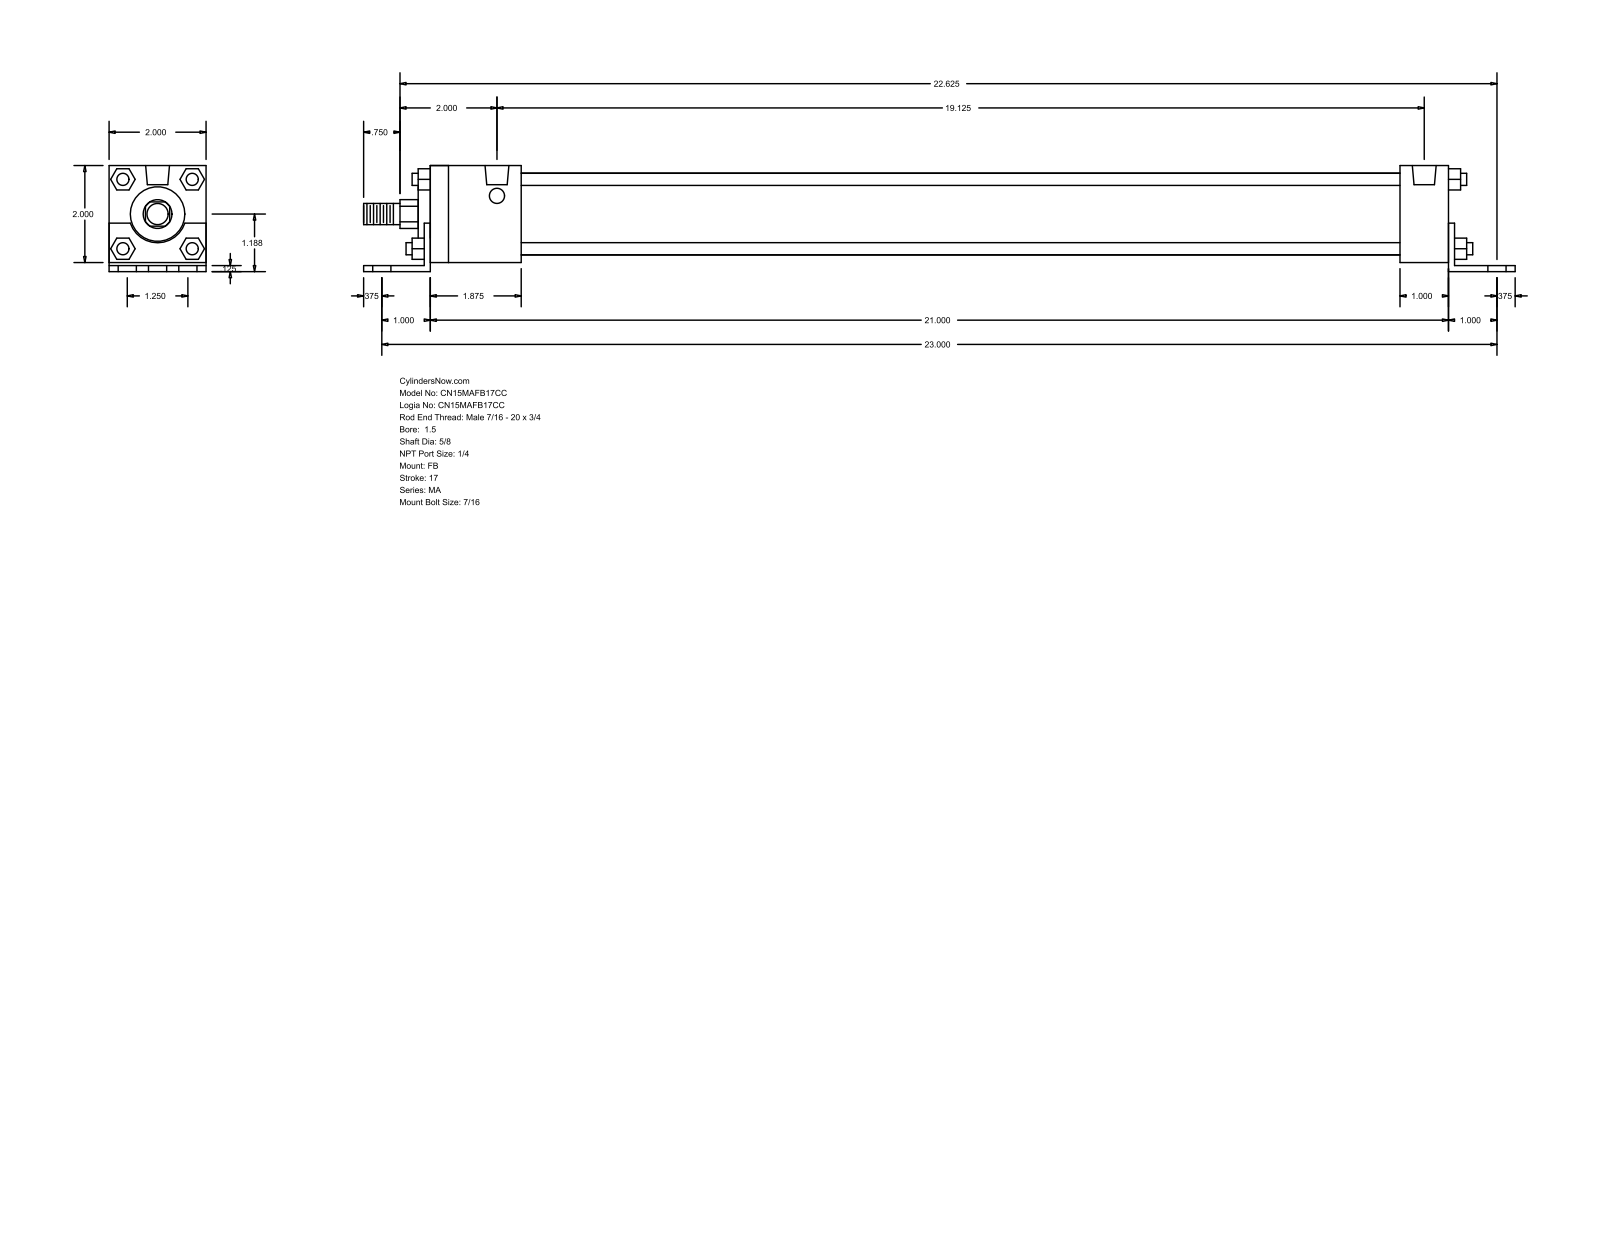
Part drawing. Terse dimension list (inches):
name: MA_FB__0150_0.625
written by: GSSL Pune (CONFIG_CONTROL_DESIGN)
unit: in
bodies: 0 solids, 140 faces (105 planar, 35 cylindrical, 0 other)
size: 23.75 × 2.187 × 2
holes: 6× ⌀0.437, 4× ⌀0.313, 2× ⌀0.492
bosses: 4× ⌀0.25, 1× ⌀1.69, 1× ⌀1.125, 1× ⌀0.625, 1× ⌀0.437
rounds: 1× R0.297, 1× R0.593
face distances: 2, 0.125, 0.187, 2.187, 0.063, 2.063, 0.125, 21.125, 0.25, 21.375
hole spacings: 0.625, 23.009, 23, 1.25, 1.625, 2.456, 19.125, 20.634
